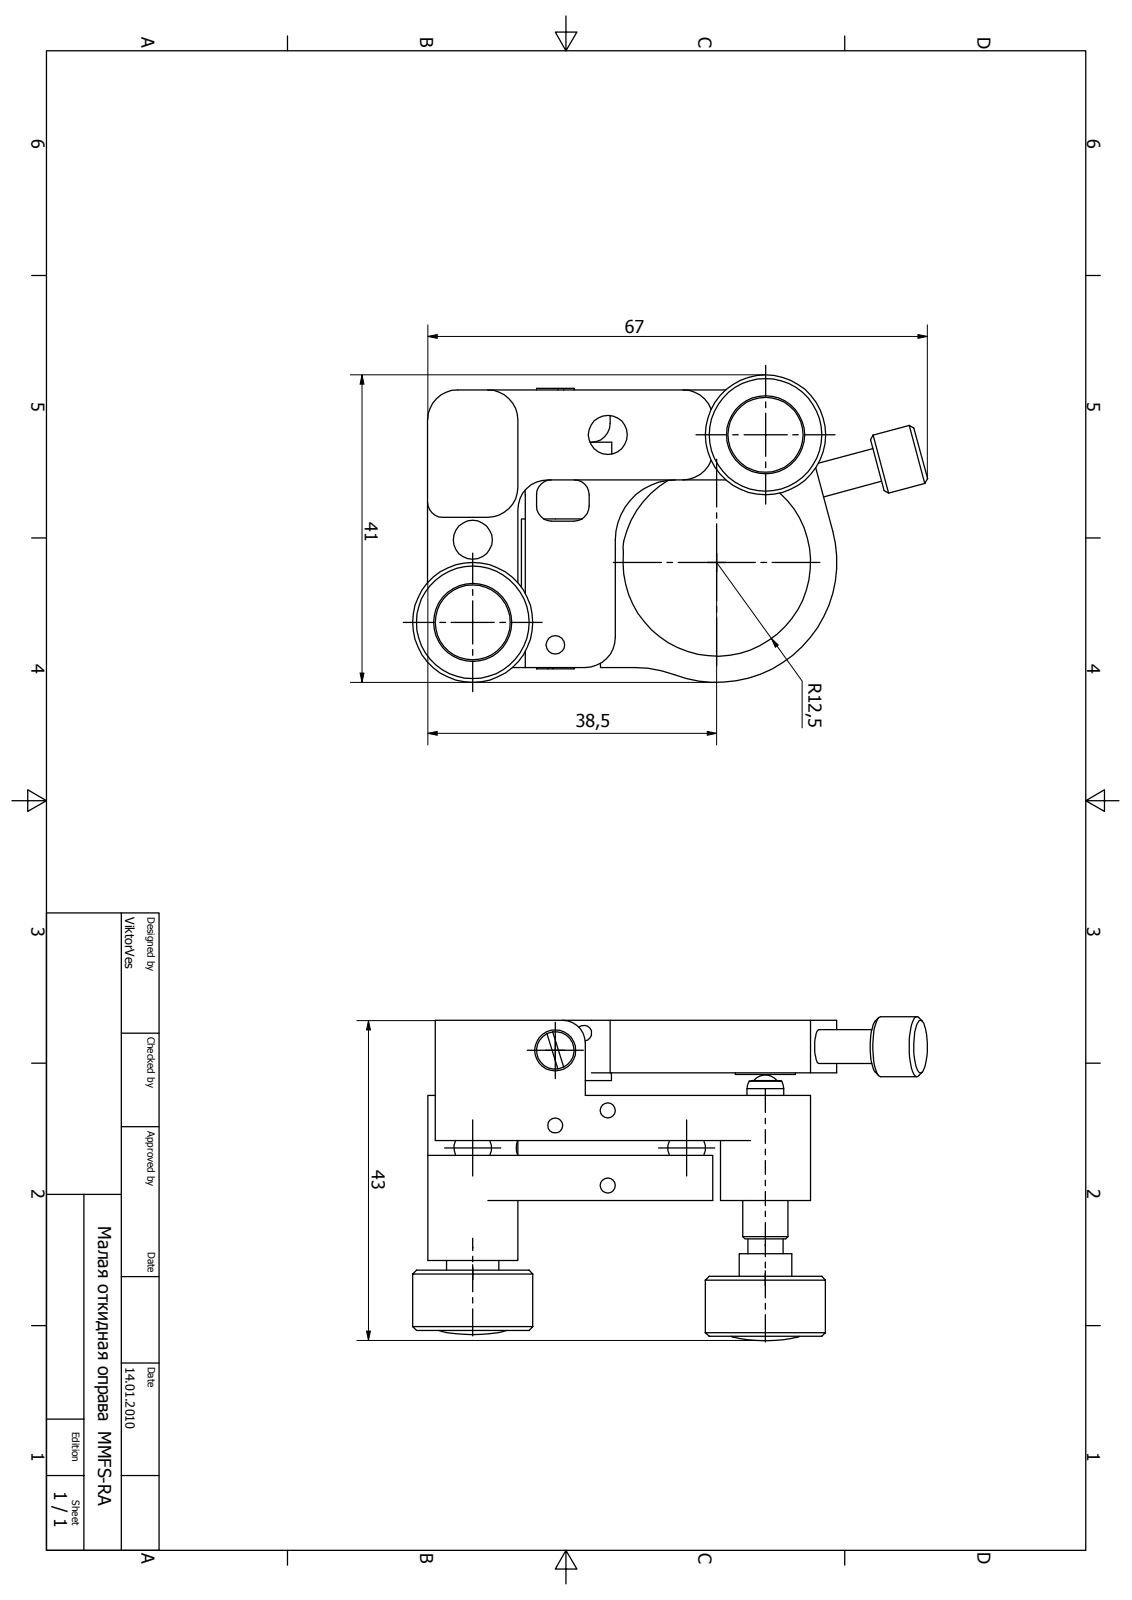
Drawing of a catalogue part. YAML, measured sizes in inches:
part_name: "Флиппер25-дюйм \\X2\\043C0430043B044B0439\\X0\\ правый; Флиппер25-дюйм \\X2\\043C0430043B044B0439\\X0\\ правый_Substitute_4; Block 01; Block 02 (+3 more)"
step_written_by: "ST-DEVELOPER v15 (AUTOMOTIVE_DESIGN)"
units: inches
bodies: {solids: 17, faces: 447, planar: 0, cylindrical: 0, other: 447}
overall_size: [2.574, 1.751, 1.28]
volume: 0.998
surface_area: 28.48
